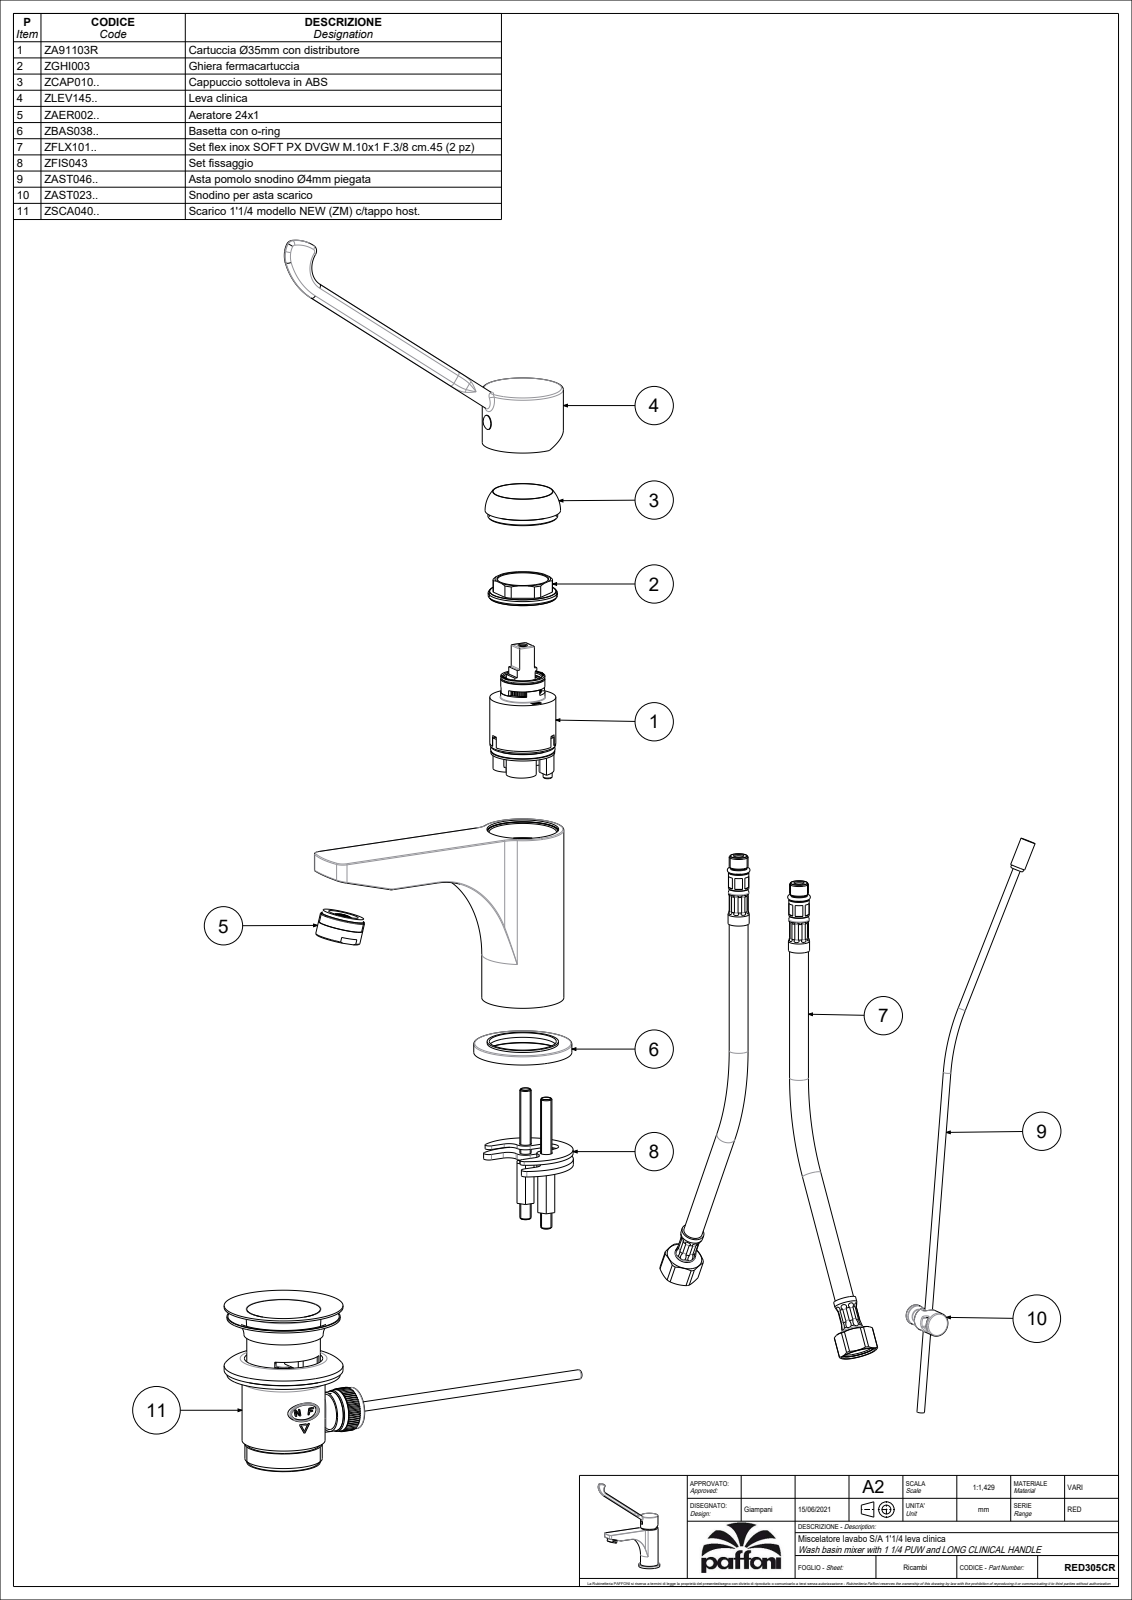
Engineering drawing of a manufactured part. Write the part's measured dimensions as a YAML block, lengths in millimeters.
part_name: "RED305CR"
step_written_by: "CREO PARAMETRIC BY PTC INC, 2020044 (CONFIG_CONTROL_DESIGN)"
units: millimeters
bodies: {solids: 6, faces: 3105, planar: 2171, cylindrical: 539, other: 395}
overall_size: [229.58, 183.37, 52]
volume: 147406
surface_area: 97815
round_holes:
  - {diameter: 9, count: 5}
  - {diameter: 5, count: 4}
  - {diameter: 4.5, count: 3}
  - {diameter: 12, count: 3}
  - {diameter: 4, count: 2}
  - {diameter: 5.5, count: 2}
  - {diameter: 6, count: 2}
  - {diameter: 6.5, count: 2}
  - {diameter: 8, count: 2}
  - {diameter: 3, count: 1}
  - {diameter: 3.3, count: 1}
  - {diameter: 3.5, count: 1}
round_bosses_or_shafts:
  - {diameter: 11.2, count: 2}
  - {diameter: 10.8, count: 2}
  - {diameter: 10, count: 2}
  - {diameter: 8.2, count: 2}
  - {diameter: 6, count: 2}
  - {diameter: 4.8, count: 2}
  - {diameter: 52, count: 1}
  - {diameter: 44.5, count: 1}
partial_cylinders:
  - {radius: 0.5, count: 88}
  - {radius: 1, count: 26}
  - {radius: 1.26, count: 14}
  - {radius: 2.05, count: 14}
  - {radius: 0.15, count: 11}
  - {radius: 0.3, count: 9}
  - {radius: 2, count: 4}
  - {radius: 7, count: 4}
face_to_face_distances: [3.5, 27.5, 31, 4.5, 13.25, 14.25, 9.75, 17.75, 15.5, 24]
hole_center_spacings: [13.6, 0.71, 2.83, 8.51, 8.6, 9.66, 9.85, 11.18]
